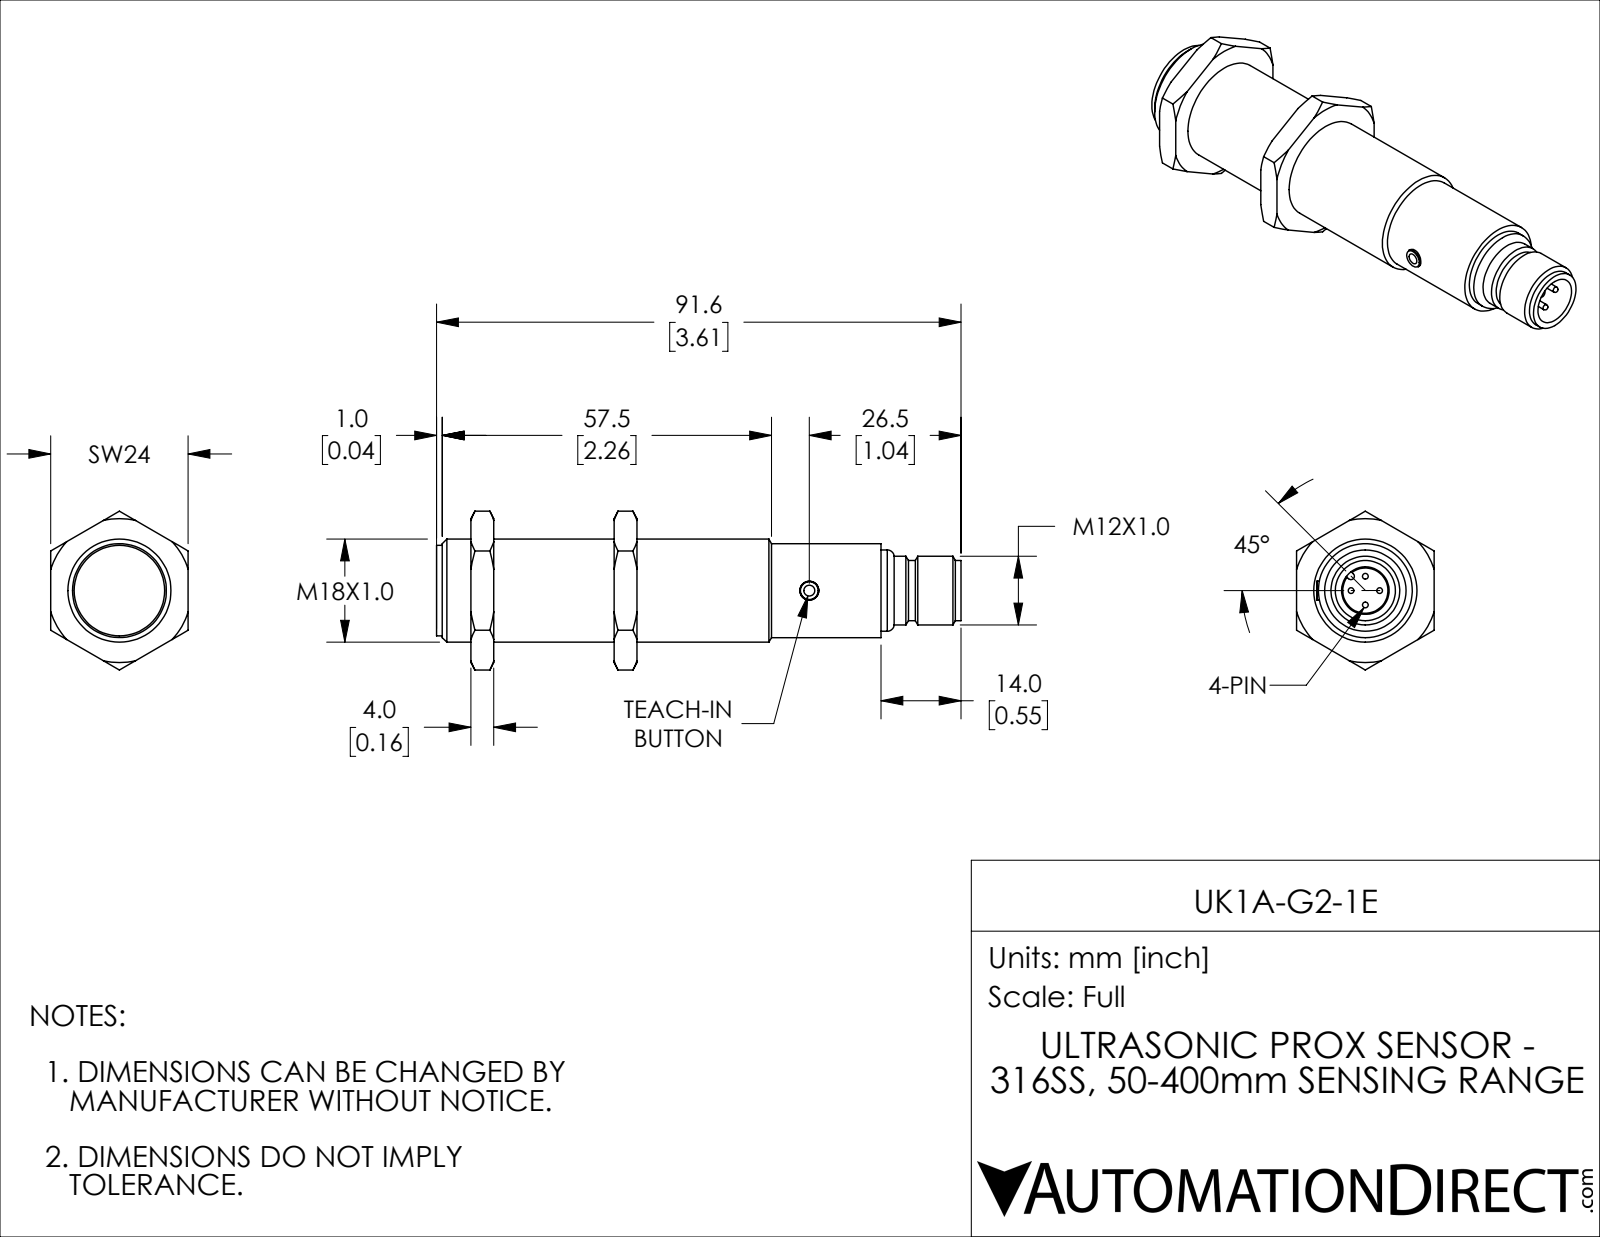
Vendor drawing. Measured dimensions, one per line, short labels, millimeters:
name: UK1A-G2-1E
written by: SolidWorks 2018 (AUTOMOTIVE_DESIGN)
unit: mm
bodies: 4 solids, 113 faces (27 planar, 35 cylindrical, 51 other)
size: 91.6 × 27.7 × 24
volume: 21 930 mm³; area: 7 723 mm²
holes: 1× ⌀3.3, 1× ⌀8.3, 1× ⌀18
bosses: 4× ⌀1, 1× ⌀16.4, 1× ⌀15.8, 1× ⌀14.2, 1× ⌀12, 1× ⌀10.5
rounds: 1× R0.6
face distances: 25, 4, 24, 29, 21, 6, 10, 31, 35, 77.6
